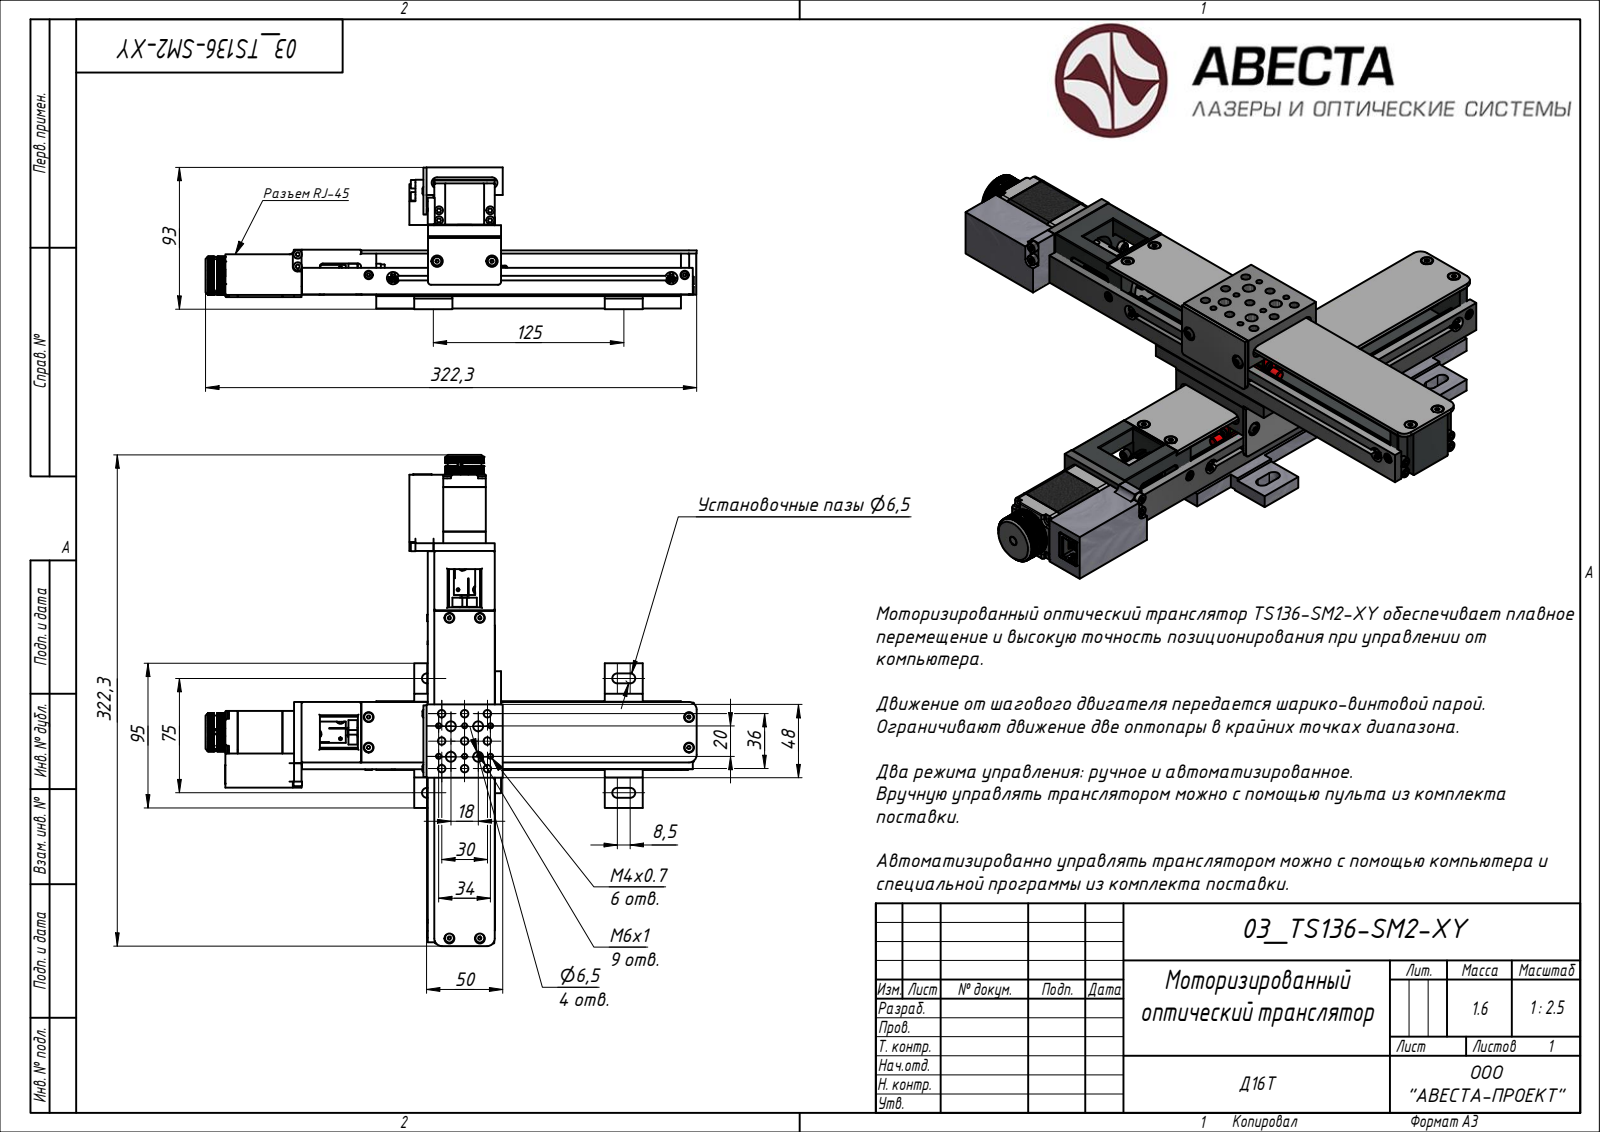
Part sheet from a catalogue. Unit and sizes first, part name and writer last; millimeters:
Units: millimetres
Overall size (bounding box): 322.3 × 322.3 × 93
Round holes (diameter × count): ⌀6.5 ×28, ⌀3.4 ×20, ⌀4.92 ×15, ⌀2.46 ×12, ⌀2.5 ×12, ⌀3.24 ×12, ⌀1.05 ×10, ⌀7.5 ×10, ⌀2.2 ×8, ⌀3.8 ×8, ⌀5 ×8, ⌀2.15 ×6
Round bosses / shafts (diameter × count): ⌀4.5 ×20, ⌀5.5 ×12, ⌀6 ×8, ⌀5.3 ×8, ⌀3 ×8, ⌀2.5 ×8, ⌀5 ×6, ⌀5.7 ×4
Partial cylindrical surfaces — rounded edges, fillets, slot ends (radius × count): R0.5 ×72, R3 ×22, R2.5 ×20, R2 ×16, R1 ×8, R3.25 ×8, R1.75 ×4, R2.4 ×4
Main face-to-face distances: 46, 2, 0.5, 27.5, 38, 44, 5.5, 29.5, 46.5, 84
Hole centre spacings: 20, 1, 16.26, 23, 297, 17, 18, 2
Volume: 596 408 mm³ · Surface area: 259 354 mm²
Bodies: 1 solid, 4415 faces (2747 planar, 1296 cylindrical, 372 other)
STEP written by: Rhino 7.34 (AUTOMOTIVE_DESIGN)
